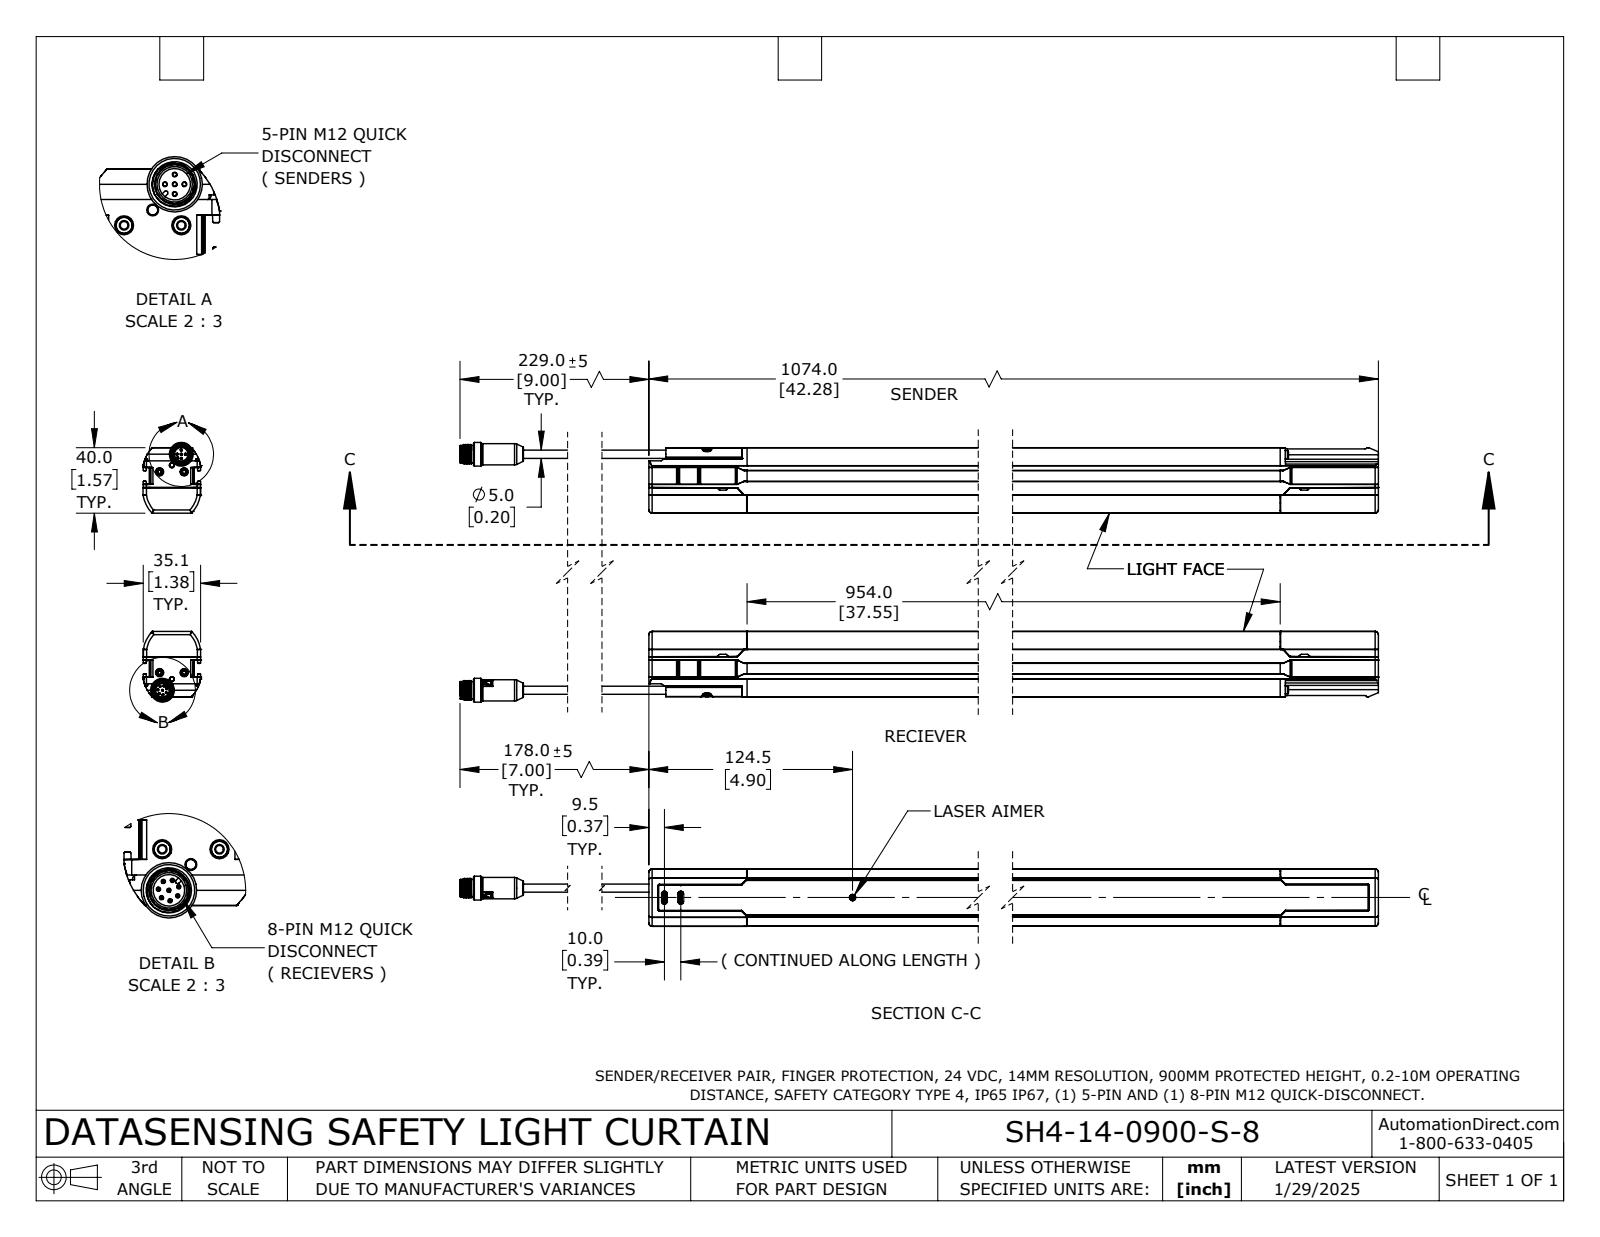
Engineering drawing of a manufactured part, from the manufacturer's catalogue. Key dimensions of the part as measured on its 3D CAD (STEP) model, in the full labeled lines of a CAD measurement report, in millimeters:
Part name (STEP PRODUCT): 957920061
STEP written by: SolidWorks 2024 (AUTOMOTIVE_DESIGN)
Units: millimetres
Bodies: 4 solids, 2616 faces (1194 planar, 784 cylindrical, 638 other)
Overall size (bounding box): 1137.3 × 158.7 × 35.1
Volume: 2 135 000 mm³ · Surface area: 382 300 mm²
Round holes (diameter × count): ⌀2 ×4, ⌀3 ×4, ⌀5 ×4, ⌀2.6 ×2, ⌀2.6 ×2, ⌀2.6 ×2, ⌀2.6 ×2, ⌀8.3 ×2, ⌀9.7 ×2, ⌀10.3 ×2, ⌀10.8 ×2, ⌀2.8 ×1
Round bosses / shafts (diameter × count): ⌀5 ×10, ⌀2.2 ×8, ⌀0.8 ×8, ⌀1 ×5, ⌀4.4 ×4, ⌀14.5 ×2, ⌀13 ×2, ⌀10.6 ×2
Partial cylindrical surfaces — rounded edges, fillets, slot ends (radius × count): R0.3 ×164, R0.4 ×66, R0.5 ×50, R0.2 ×36, R0.8 ×20, R0.8 ×12, R1.5 ×10, R2 ×10
Main face-to-face distances: 38, 114.2, 4, 31, 76.2, 35, 152.2, 27.1, 26.2, 117.7
Hole centre spacings: 22, 136.6, 138.3, 10.9, 15, 17.1, 122.7, 123.6
